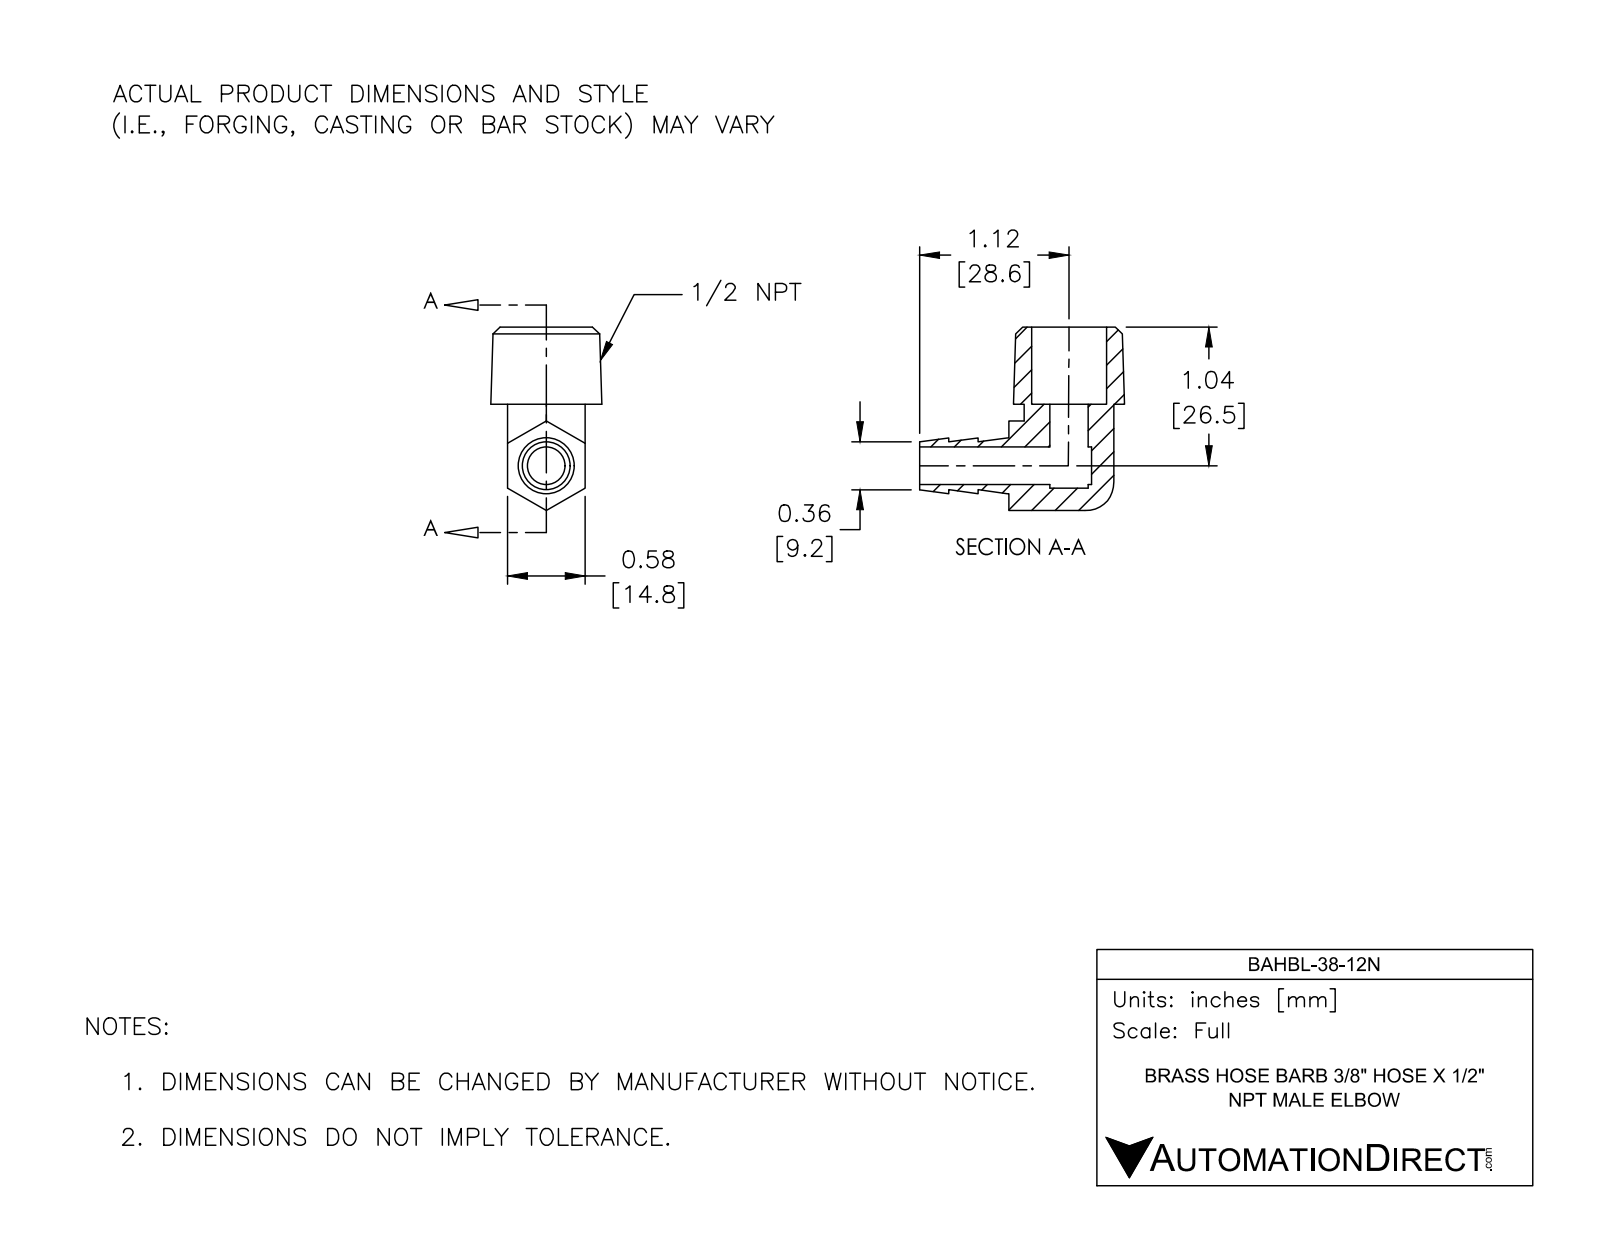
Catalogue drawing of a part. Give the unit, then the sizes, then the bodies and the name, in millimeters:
Units: millimetres
Overall size (bounding box): 39.2 × 35.1 × 21.2
Round holes (diameter × count): ⌀7.2 ×1, ⌀7.3 ×1, ⌀14.3 ×1
Round bosses / shafts (diameter × count): ⌀10.7 ×1
Partial cylindrical surfaces — rounded edges, fillets, slot ends (radius × count): R6.4 ×2
Main face-to-face distances: 14.8, 14.8, 14.7, 5.6, 16, 30.8, 15.8, 32.8, 17.1, 21.7
Volume: 6 470 mm³ · Surface area: 4 868 mm²
Bodies: 1 solid, 41 faces (19 planar, 12 cylindrical, 10 other)
Part name (STEP PRODUCT): BAHBL-38-12N
STEP written by: SolidWorks 2017 (AUTOMOTIVE_DESIGN)
